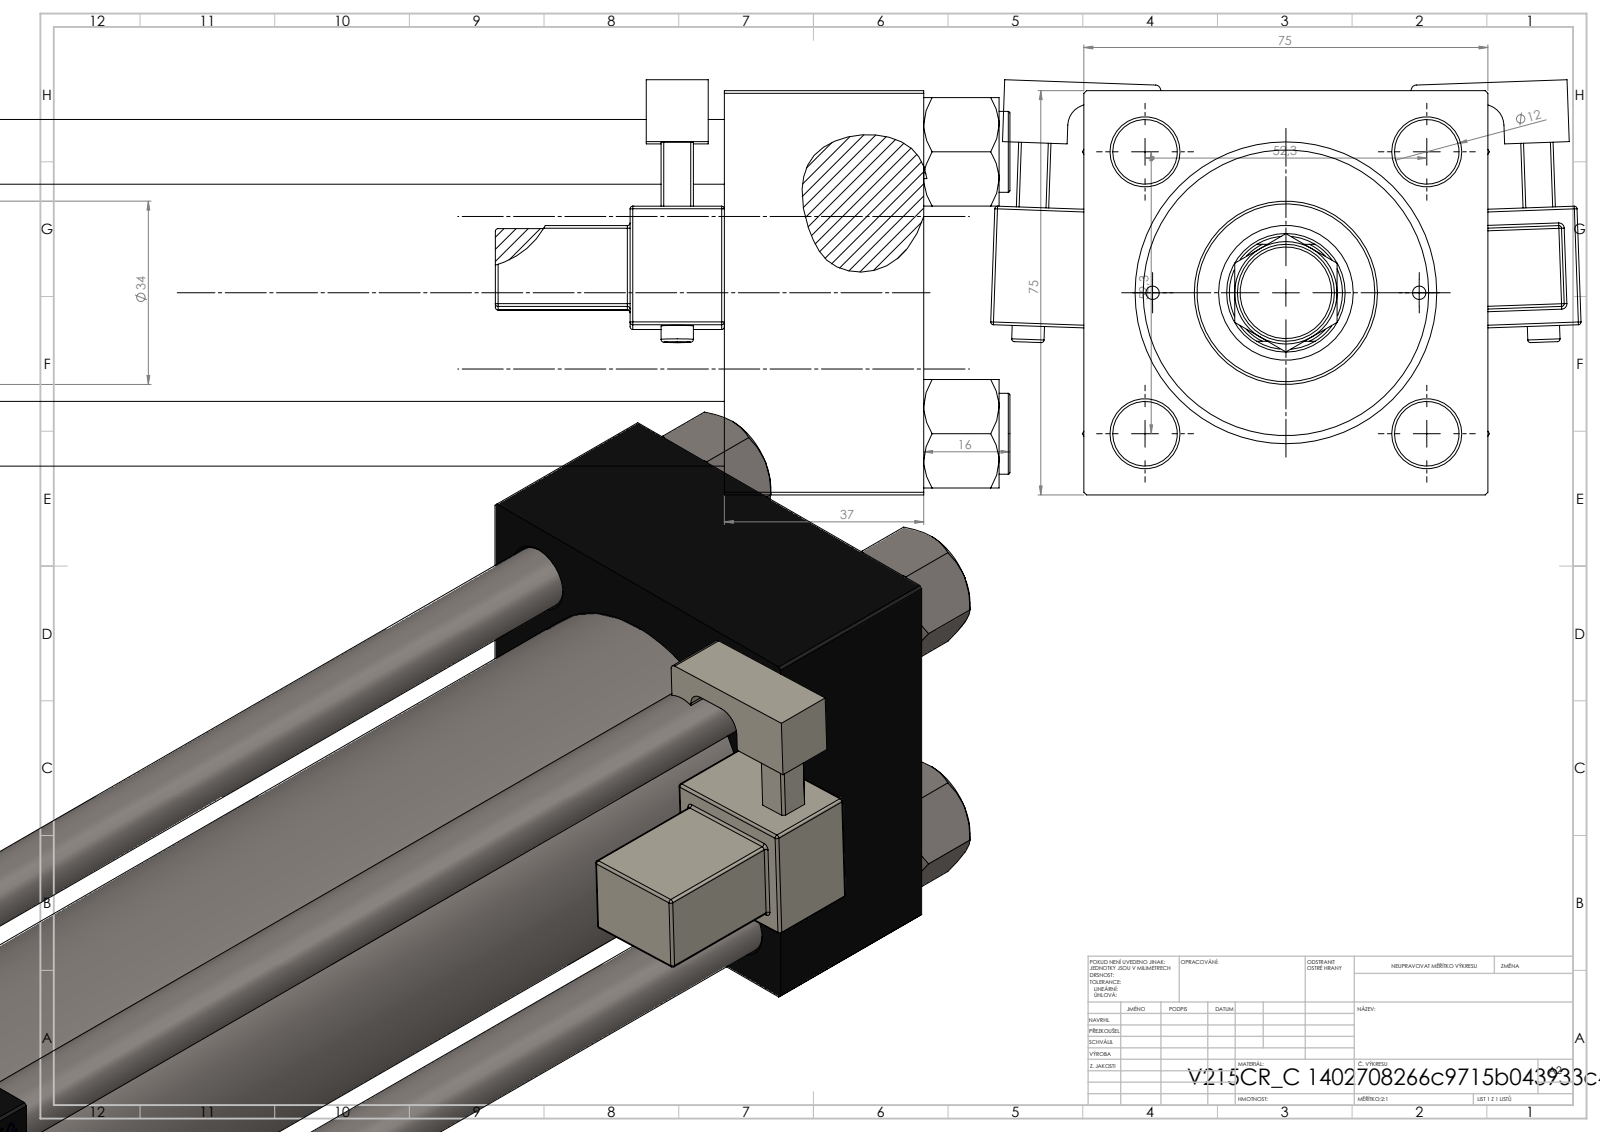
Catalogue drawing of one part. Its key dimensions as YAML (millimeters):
part_name: "MFA; V215CR_VCP_C; V215CR_MSU; V215_VC_A (+3 more)"
step_written_by: "SolidWorks 2019 (CONFIG_CONTROL_DESIGN)"
units: millimeters
bodies: {solids: 14, faces: 1360, planar: 602, cylindrical: 154, other: 604}
overall_size: [368, 109.57, 77.03]
volume: 892615
surface_area: 239739
round_holes:
  - {diameter: 12, count: 4}
  - {diameter: 2.5, count: 2}
  - {diameter: 7, count: 2}
  - {diameter: 20.96, count: 2}
  - {diameter: 30, count: 2}
  - {diameter: 10.5, count: 1}
  - {diameter: 22, count: 1}
  - {diameter: 25, count: 1}
  - {diameter: 41, count: 1}
  - {diameter: 50, count: 1}
  - {diameter: 53, count: 1}
round_bosses_or_shafts:
  - {diameter: 15, count: 4}
  - {diameter: 6, count: 2}
  - {diameter: 56, count: 1}
  - {diameter: 34, count: 1}
  - {diameter: 18, count: 1}
  - {diameter: 11, count: 1}
partial_cylinders:
  - {radius: 0.5, count: 48}
  - {radius: 1, count: 2}
  - {radius: 2.5, count: 2}
  - {radius: 4, count: 2}
  - {radius: 10.5, count: 1}
face_to_face_distances: [75, 37, 294, 257, 235, 198, 59, 265.3, 228.3, 30.3]
hole_center_spacings: [26.19, 36.98, 52.3, 57.22, 24.75, 73.96, 49.5, 233.5]
